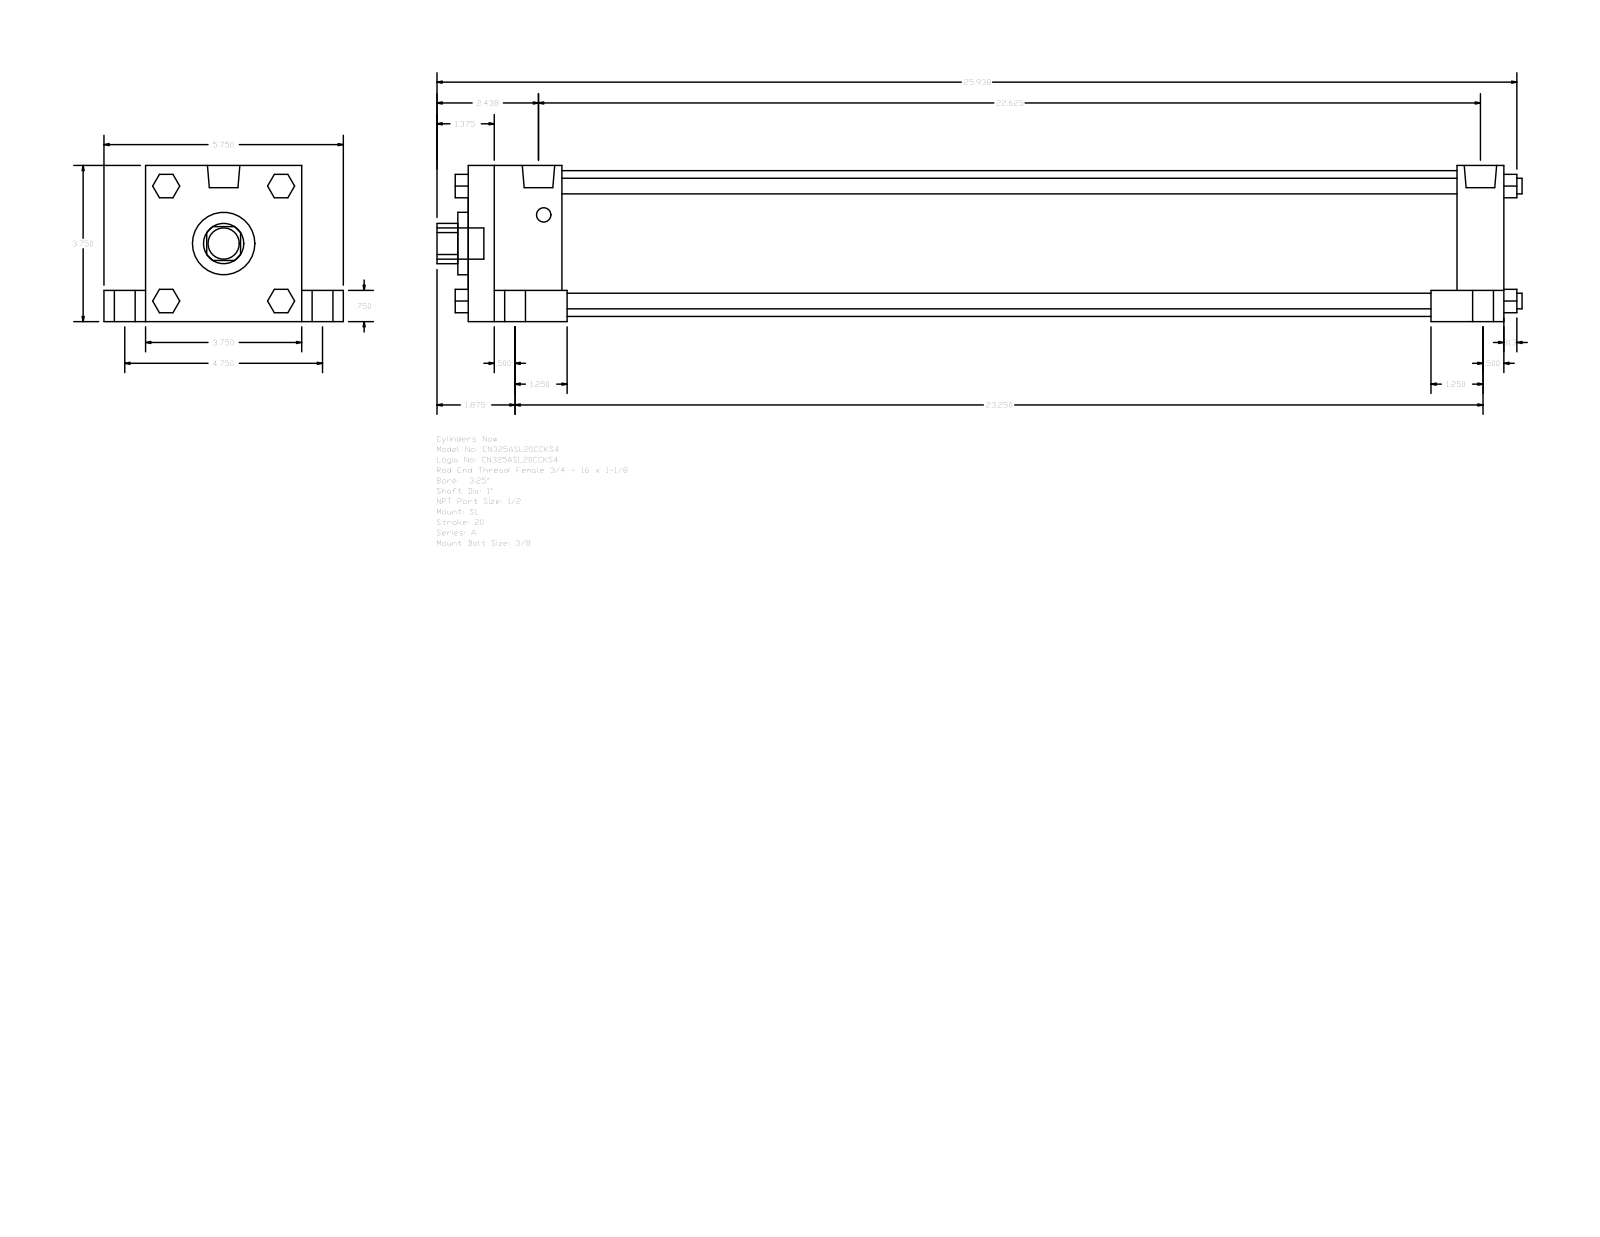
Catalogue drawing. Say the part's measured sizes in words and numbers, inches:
The part is named "A_SL__0325_1". Its 3-D file was written by "GSSL Pune (CONFIG_CONTROL_DESIGN)". It is 0 solids with 150 faces: 114 planar, 36 cylindrical and 0 other. Overall it measures 26.063 by 5.75 by 3.75 inches. Round holes: 1 of diameter 1, 1 of diameter 1.5, 1 of diameter 3.5. Round bosses or shafts: 5 of diameter 0.75, 4 of diameter 0.5, 4 of diameter 0.375, 4 of diameter 0.344, 2 of diameter 0.778. Partial cylindrical surfaces (rounded edges, fillets, slot ends): 1 of radius 0.484. The main face-to-face distances are 3.75, 24.875, 0.75, 1, 4.75, 3, 2.25, 23.75, 21.5, 22.625.
